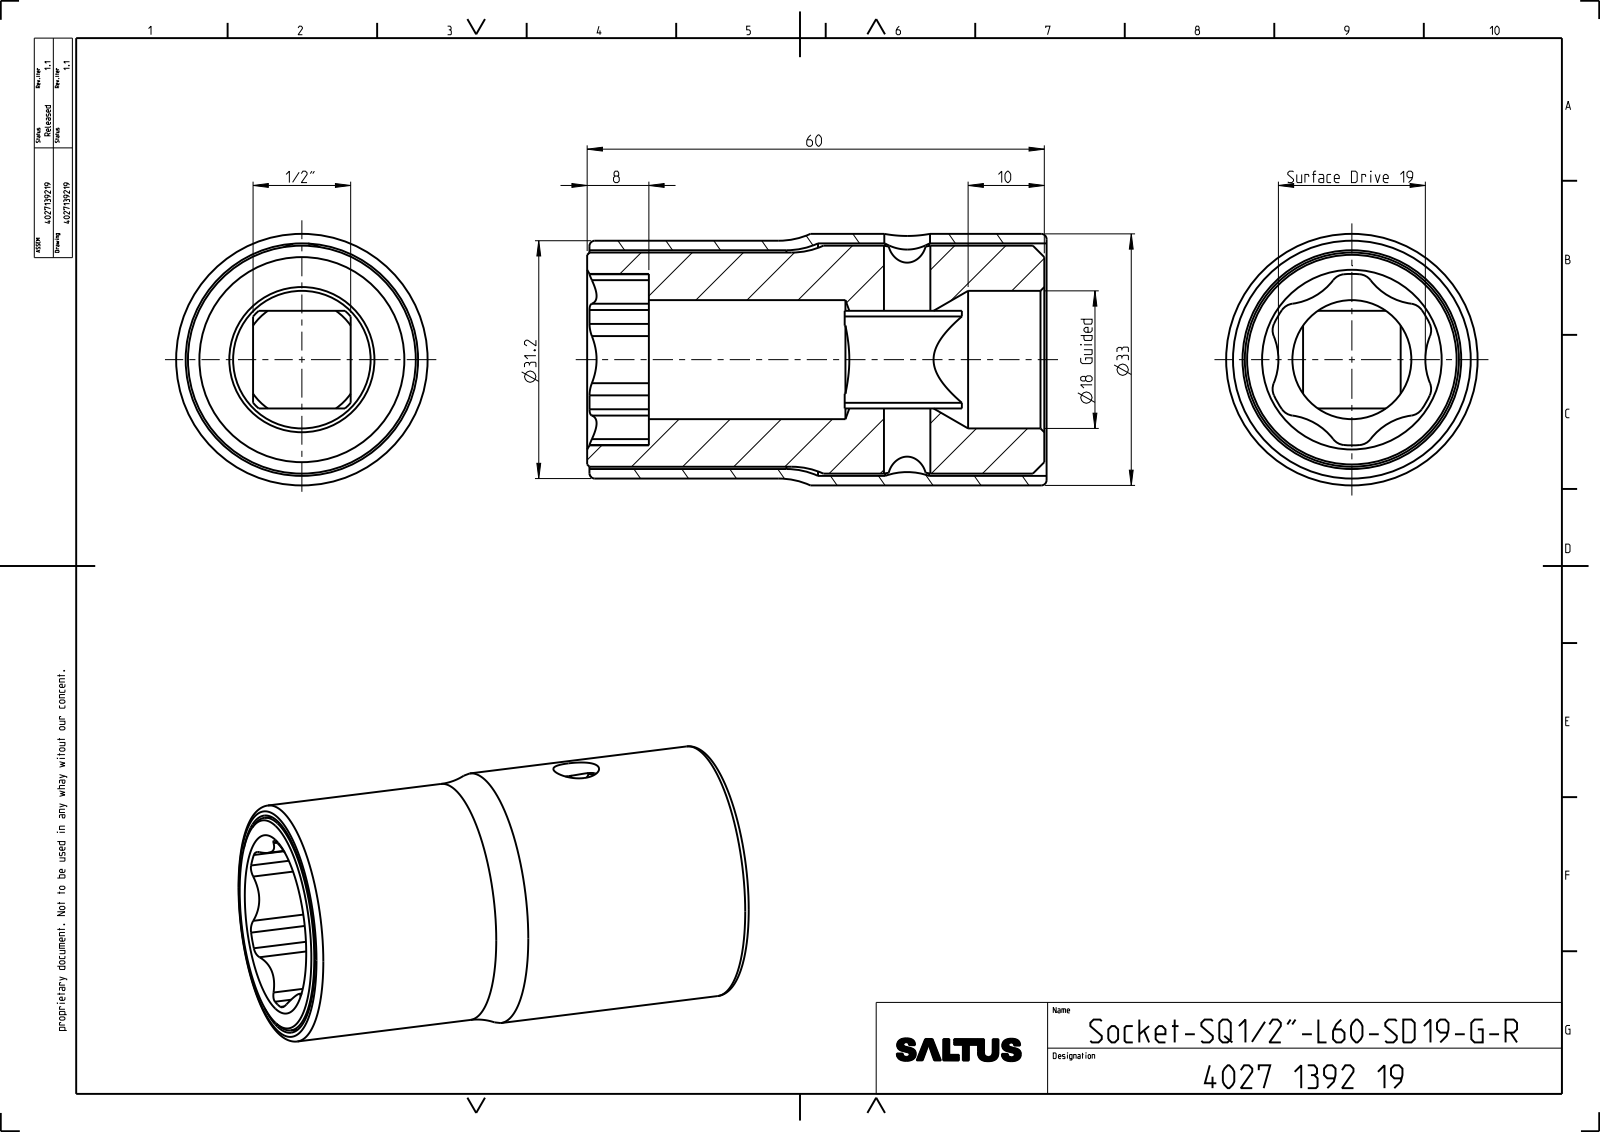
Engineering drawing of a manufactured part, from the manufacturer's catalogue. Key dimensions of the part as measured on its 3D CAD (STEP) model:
Part name (STEP PRODUCT): 4027021922; 4027299533; 4027139219_ASM
STEP written by: CREO PARAMETRIC BY PTC INC, 2022414 (CONFIG_CONTROL_DESIGN)
Units: millimetres
Bodies: 2 solids, 94 faces (13 planar, 54 cylindrical, 27 other)
Overall size (bounding box): 60.3 × 33 × 33
Volume: 32 912 mm³ · Surface area: 21 566 mm²
Round holes (diameter × count): ⌀6 ×1, ⌀6.09 ×1, ⌀15.62 ×1, ⌀18.05 ×1, ⌀28.7 ×1, ⌀30.5 ×1
Round bosses / shafts (diameter × count): ⌀33 ×1, ⌀31.2 ×1, ⌀29.9 ×1, ⌀28.1 ×1
Partial cylindrical surfaces — rounded edges, fillets, slot ends (radius × count): R2 ×12, R8.1 ×6, R8.55 ×1, R11.25 ×1
Main face-to-face distances: 12.82, 60, 51.9, 8.1, 52.2, 60.3, 59.7, 7.8, 26.5, 26.2
